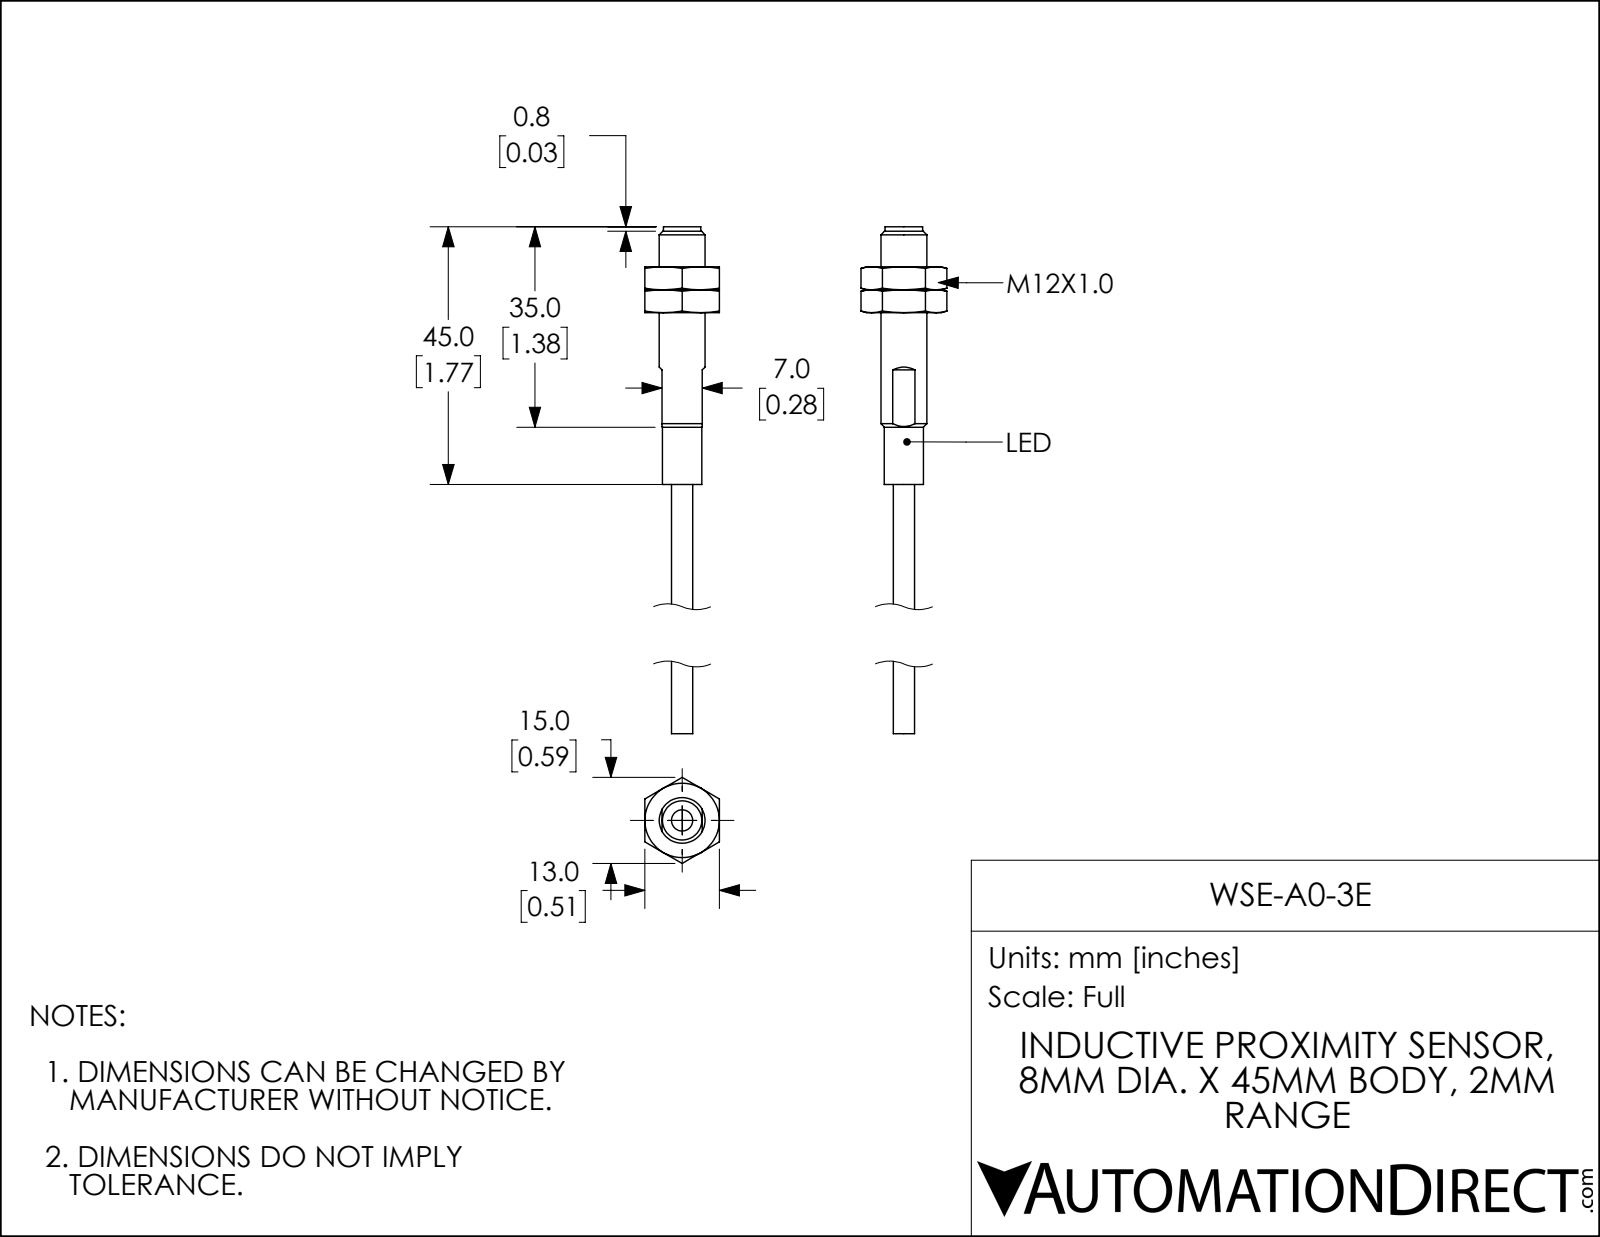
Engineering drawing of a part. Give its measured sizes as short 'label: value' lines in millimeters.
name: WSE-A0-3E
written by: SolidWorks 2017 (AUTOMOTIVE_DESIGN)
unit: mm
bodies: 3 solids, 61 faces (25 planar, 6 cylindrical, 30 other)
size: 95.9 × 15 × 13
volume: 3 470 mm³; area: 2 690 mm²
holes: 1× ⌀6.9
bosses: 1× ⌀8, 1× ⌀6.9, 1× ⌀6.6, 1× ⌀3.7
face distances: 13, 4, 8, 10, 3, 7, 15, 11, 30, 34
